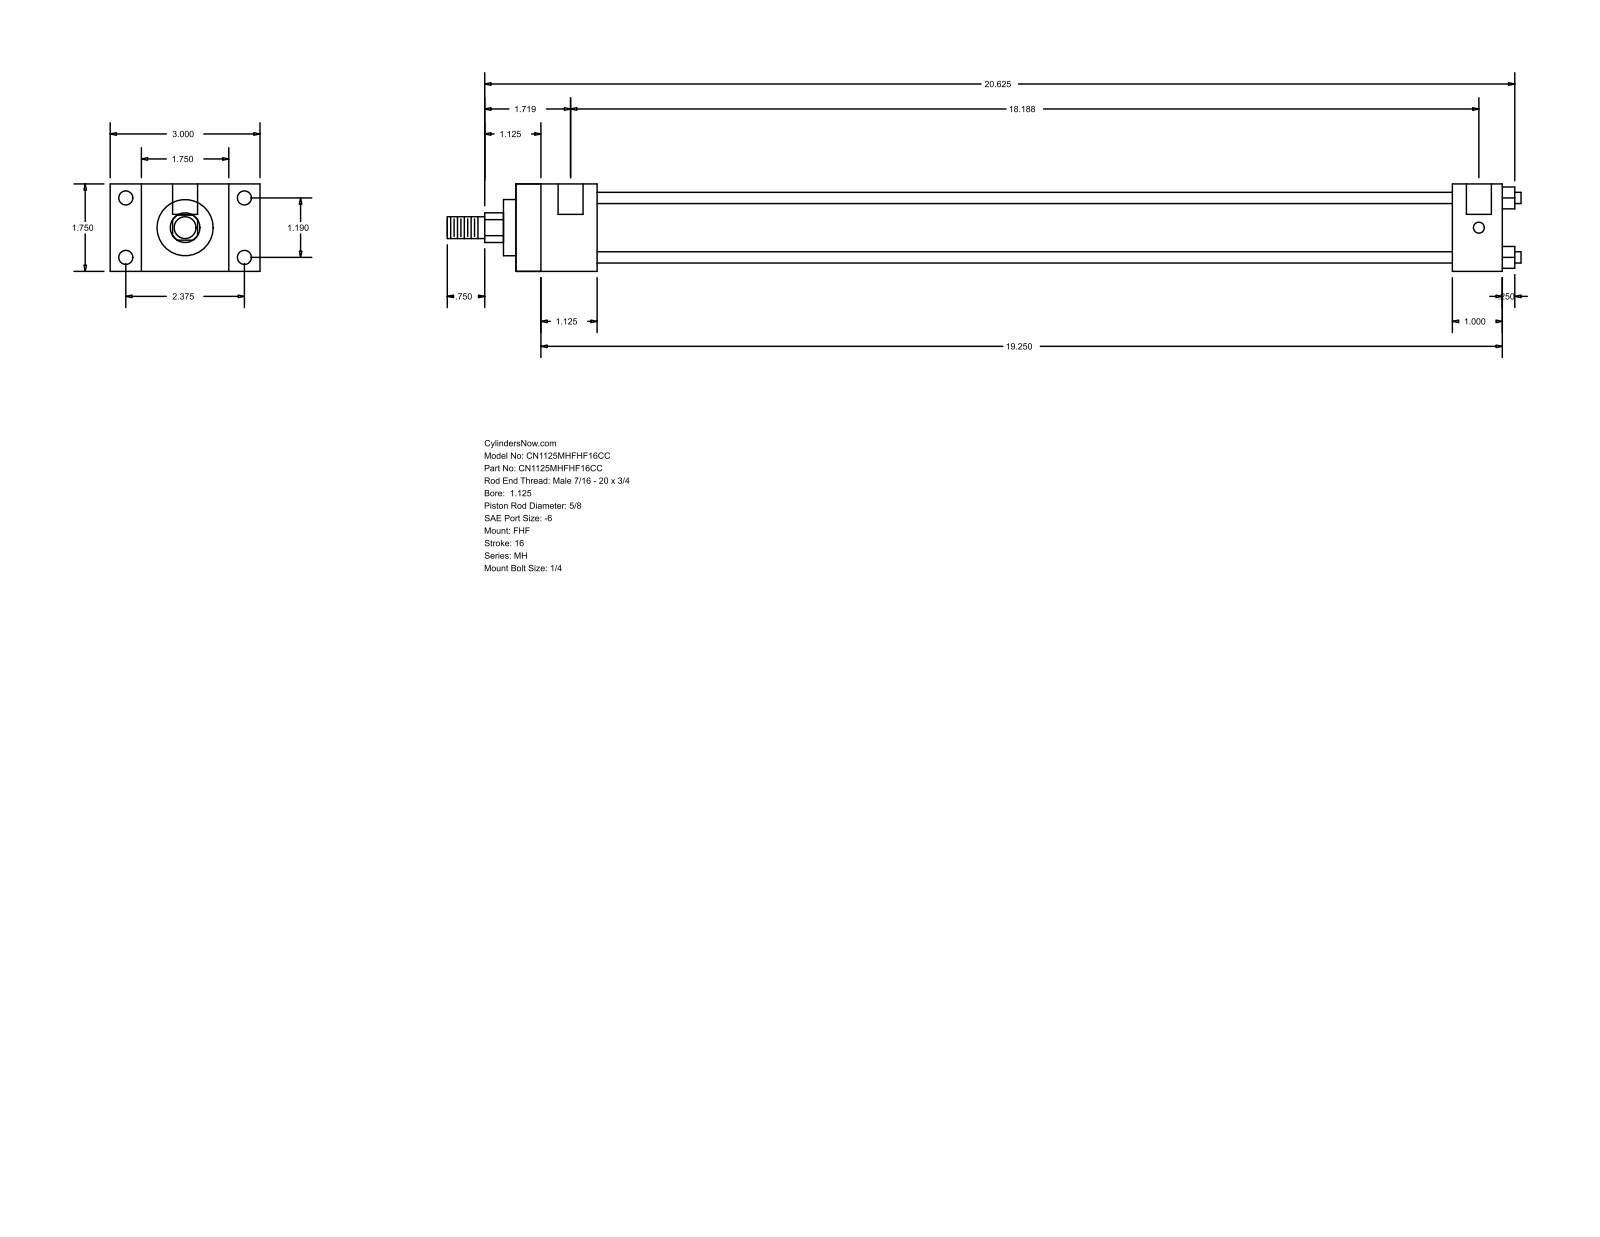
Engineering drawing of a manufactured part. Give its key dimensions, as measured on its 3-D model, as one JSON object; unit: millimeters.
{"part_name": "MH_FHF__0112_0.625", "step_written_by": "GSSL Pune (CONFIG_CONTROL_DESIGN)", "units": "millimeters", "bodies": {"solids": 0, "faces": 88, "planar": 60, "cylindrical": 28, "other": 0}, "overall_size": [546.1, 76.2, 44.45], "round_holes": [[5.56, 4], [7.14, 4], [12.7, 2]], "round_bosses_or_shafts": [[5.71, 4], [34.92, 1], [28.57, 1], [15.88, 1], [11.11, 1]], "partial_cylinders_radius": [[7.54, 1]], "face_to_face_distances": [44.46, 15.87, 60.33, 41.27, 76.2, 501.64, 460.37, 25.4, 476.24, 434.97], "hole_center_spacings": [30.22, 60.32, 67.47, 458.79, 3.17, 461.96]}
